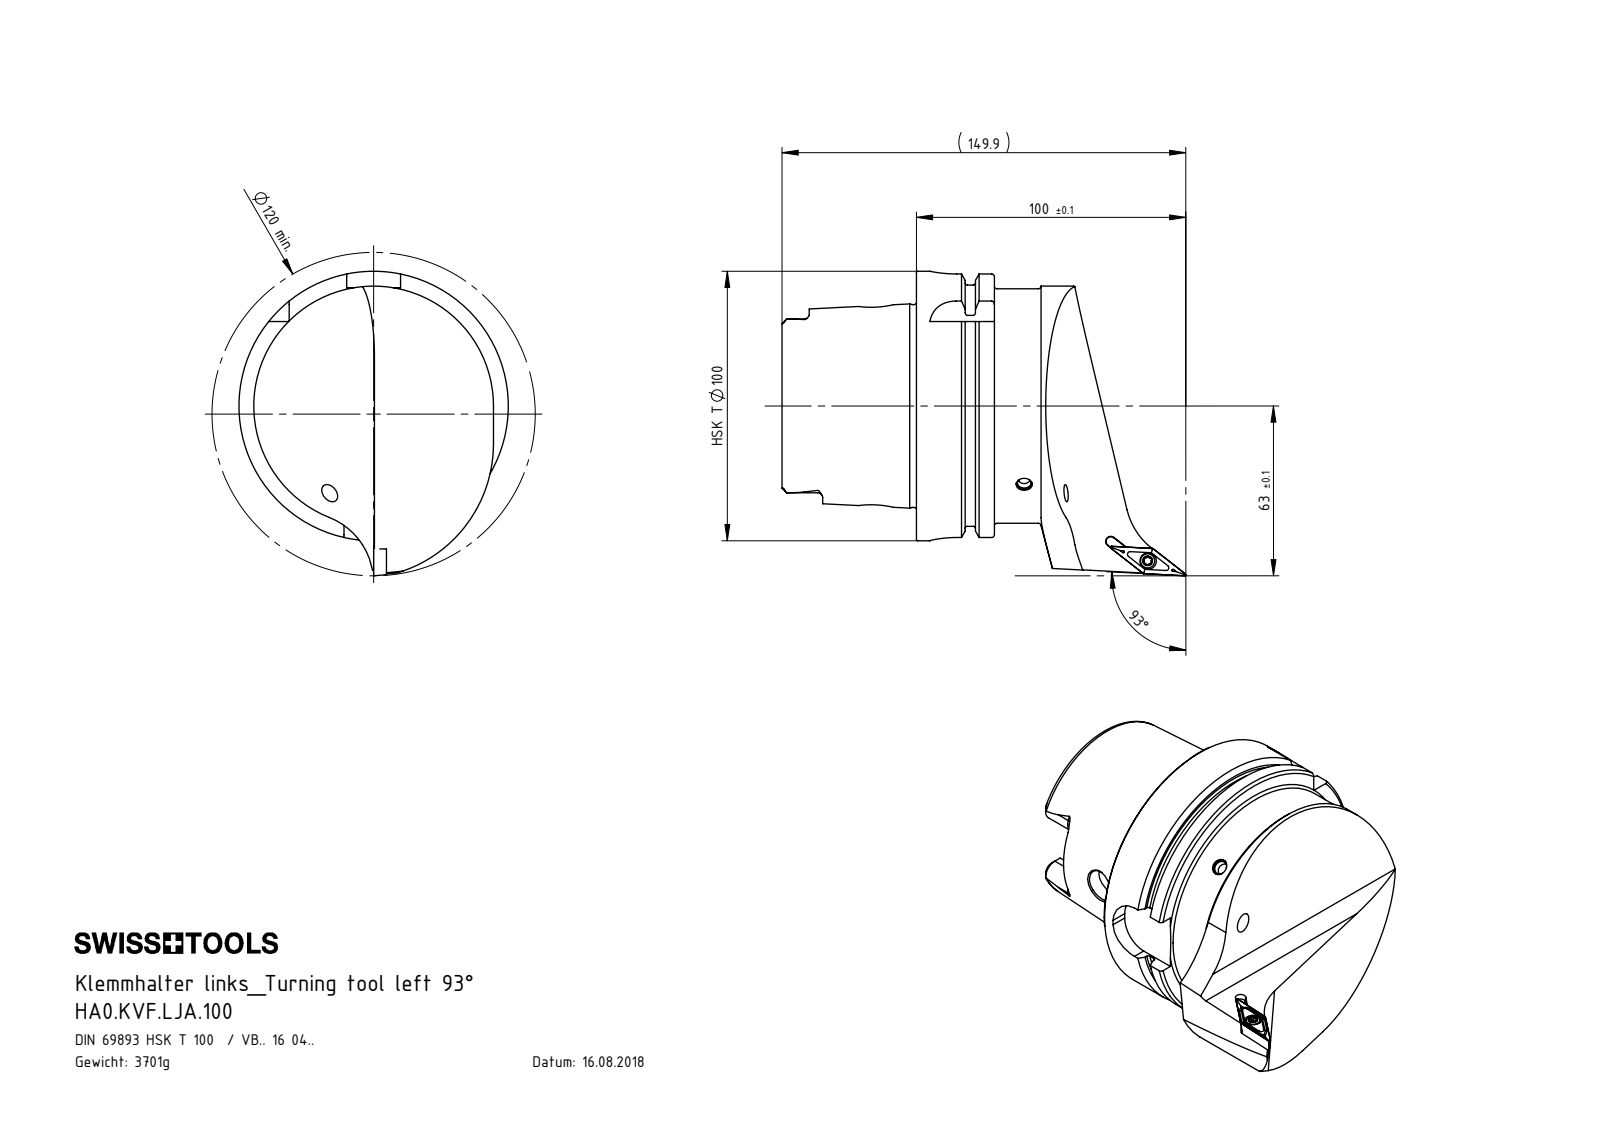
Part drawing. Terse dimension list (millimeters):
name: VBMT160404; HA0.KVF.LJA.100; WCB-ER2.001.009_A; KVT_MB_600_060 (+1 more)
written by: SolidWorks 2017 (AUTOMOTIVE_DESIGN)
unit: mm
bodies: 5 solids, 238 faces (77 planar, 63 cylindrical, 98 other)
size: 149.91 × 113 × 100
volume: 472 462 mm³; area: 64 923 mm²
holes: 3× ⌀5, 2× ⌀12, 1× ⌀3.3, 1× ⌀4.4, 1× ⌀6, 1× ⌀6.1, 1× ⌀10, 1× ⌀22.5, 1× ⌀26, 1× ⌀53, 1× ⌀63
bosses: 1× ⌀100, 1× ⌀91.95, 1× ⌀87, 1× ⌀75.26, 1× ⌀6, 1× ⌀5.25, 1× ⌀4
rounds: 6× R0.34, 6× R0.59, 6× R1.9, 4× R10, 2× R0.15, 2× R4.83, 2× R4.88, 1× R1.75
face distances: 12.45, 28.95, 16.5, 49.9, 62.35, 78.85, 87.8, 78.2, 28.3, 15.85
hole spacings: 97.53, 97.74
